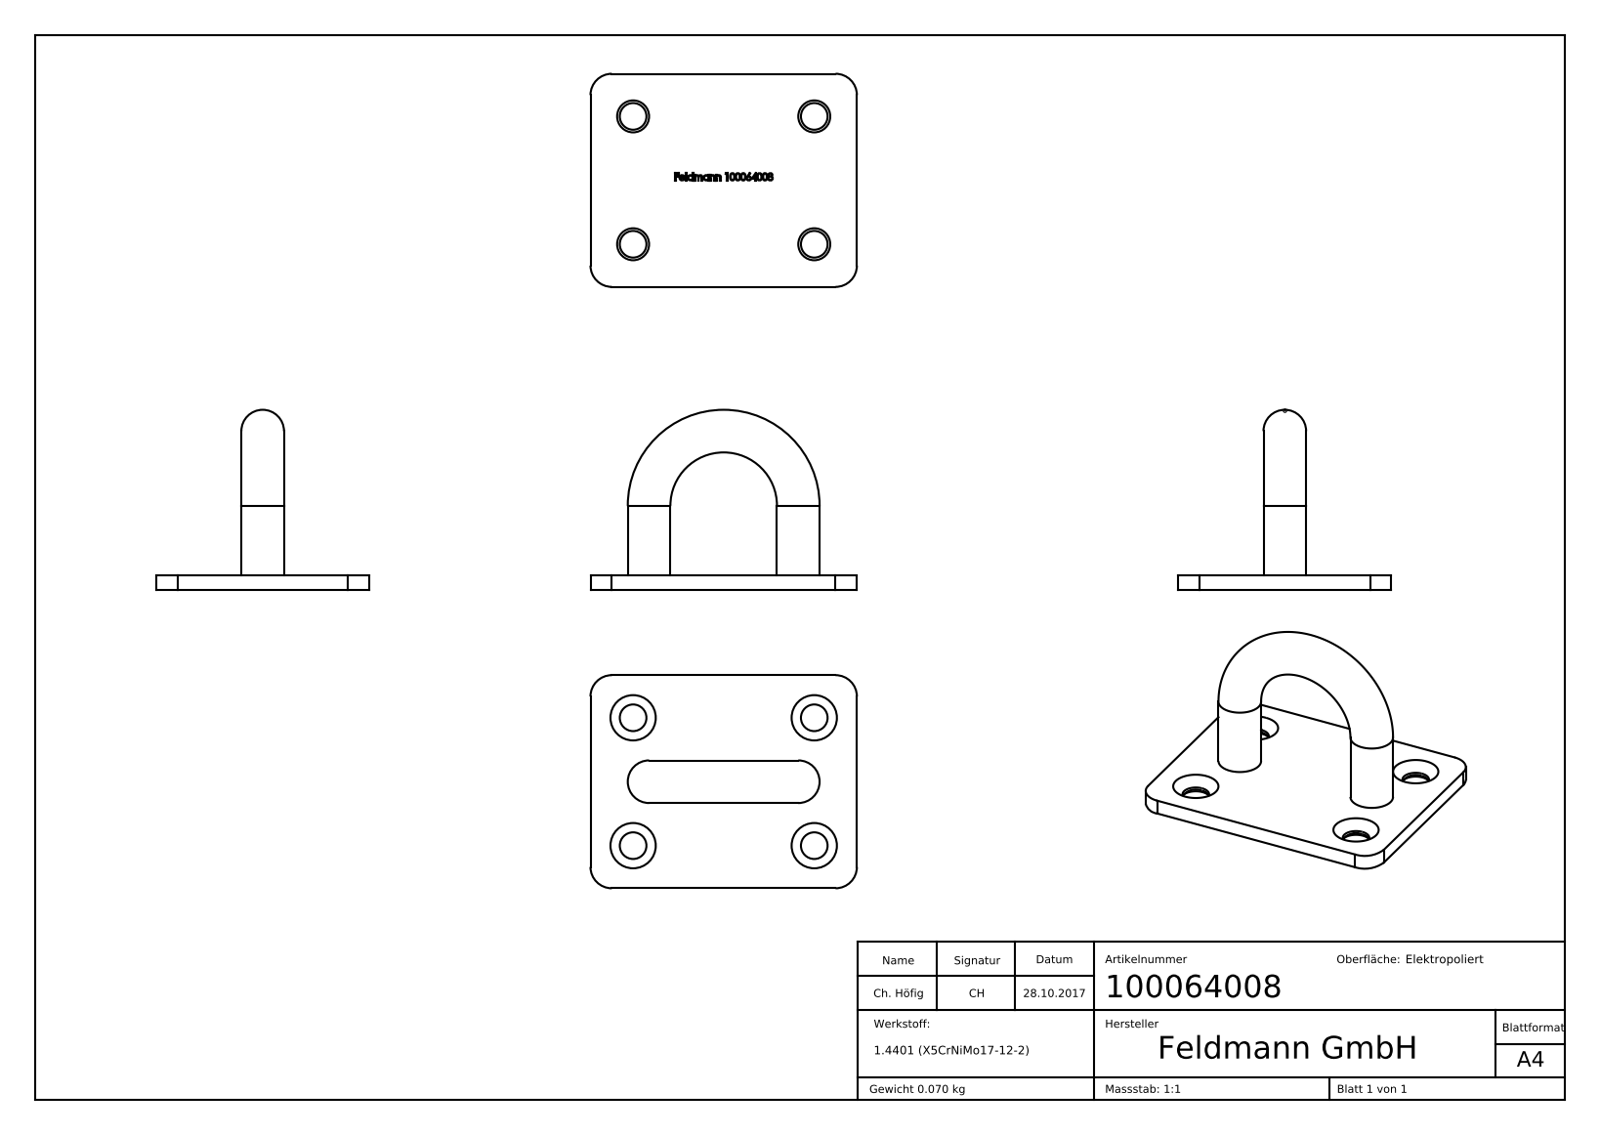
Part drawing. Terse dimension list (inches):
name: 10006400X Konfig
written by: SolidWorks 2015 (CONFIG_CONTROL_DESIGN)
unit: in
bodies: 1 solid, 264 faces (111 planar, 16 cylindrical, 137 other)
size: 1.969 × 1.575 × 1.331
volume: 0.533 in³; area: 9.429 in²
holes: 4× ⌀0.197
bosses: 2× ⌀0.315
rounds: 4× R0.157
face distances: 0.11, 1.575, 1.969, 0.106, 0.787, 0.015, 0.08, 0.05, 0.511, 0.065
hole spacings: 0.945, 1.339, 1.639
